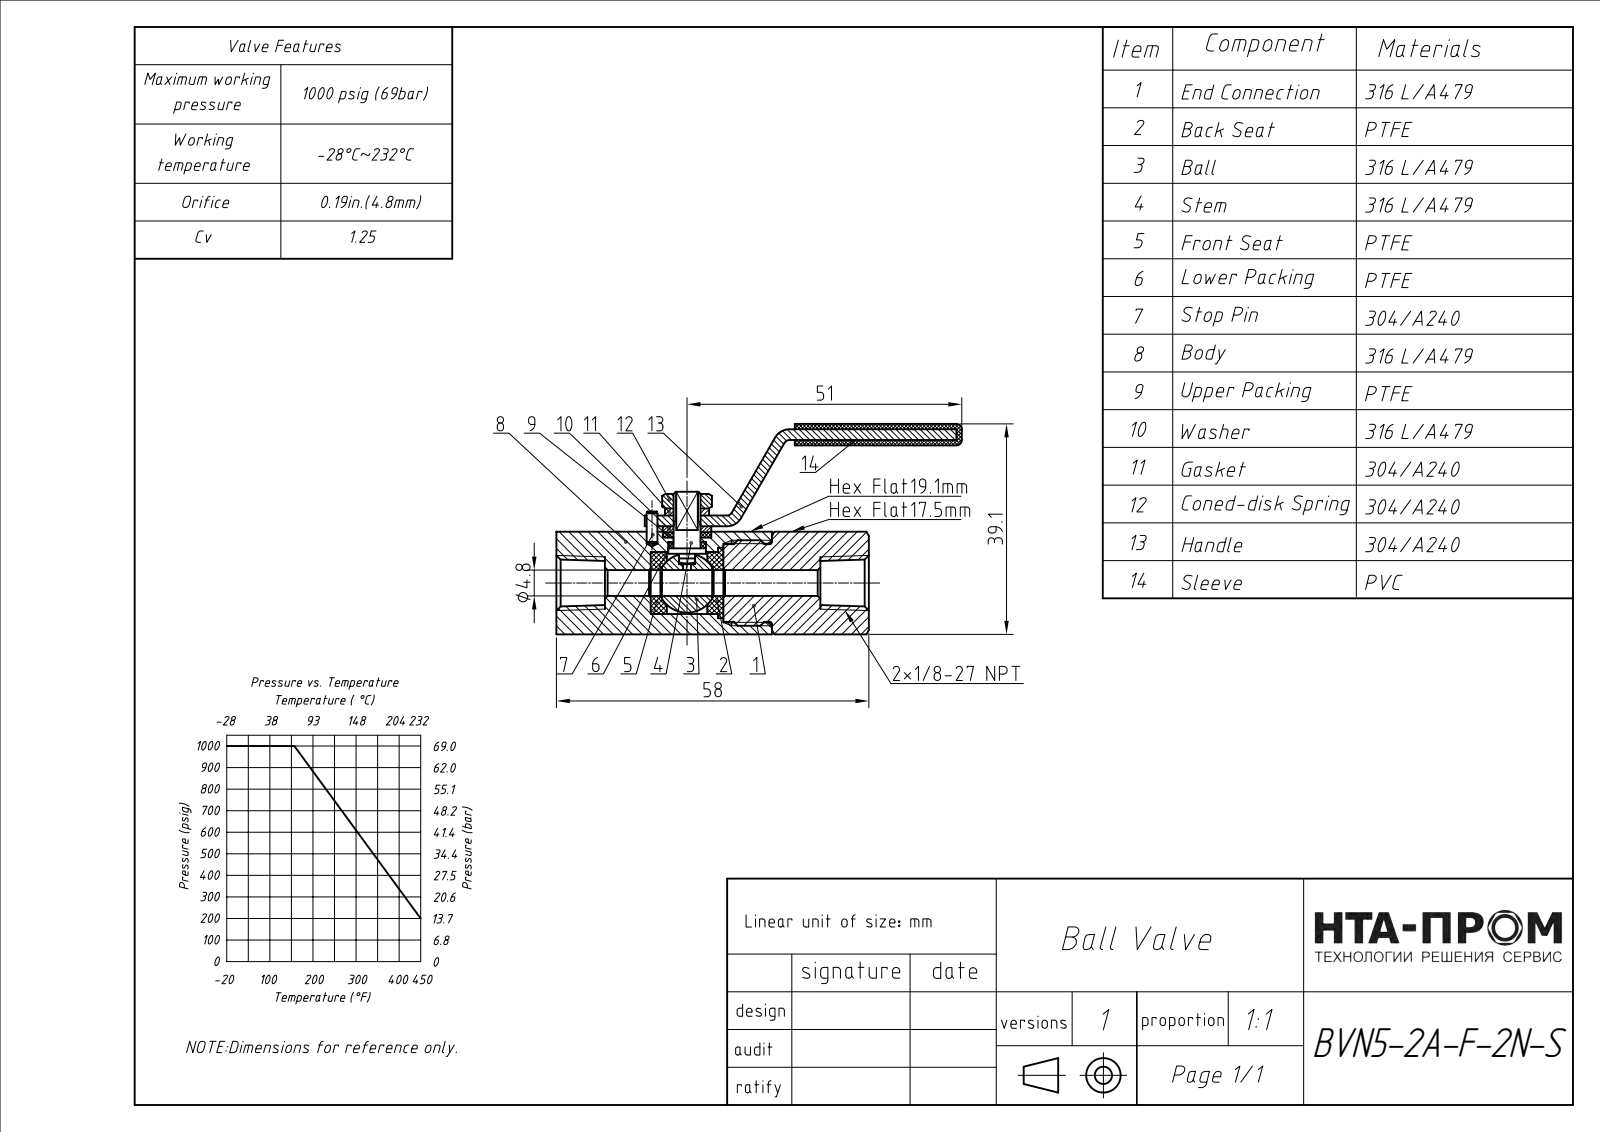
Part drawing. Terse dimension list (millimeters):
name: BVN5-2A-F-2N-S; BVN5; COMPOUND
written by: FreeCAD (AUTOMOTIVE_DESIGN)
unit: mm
bodies: 5 solids, 124 faces (55 planar, 39 cylindrical, 30 other)
size: 74.1 × 37.98 × 22.05
volume: 17 503 mm³; area: 9 682 mm²
holes: 1× ⌀4.8, 1× ⌀11.5, 1× ⌀14.6
bosses: 1× ⌀15.87, 1× ⌀14.4, 1× ⌀8.2, 1× ⌀7, 1× ⌀5
rounds: 4× R0.6, 4× R1, 3× R5, 2× R0.5, 2× R2, 2× R3, 1× R8, 1× R9.53
face distances: 19.1, 2, 17.5, 37.98, 18.88, 35.98, 16.88, 18, 16, 31
